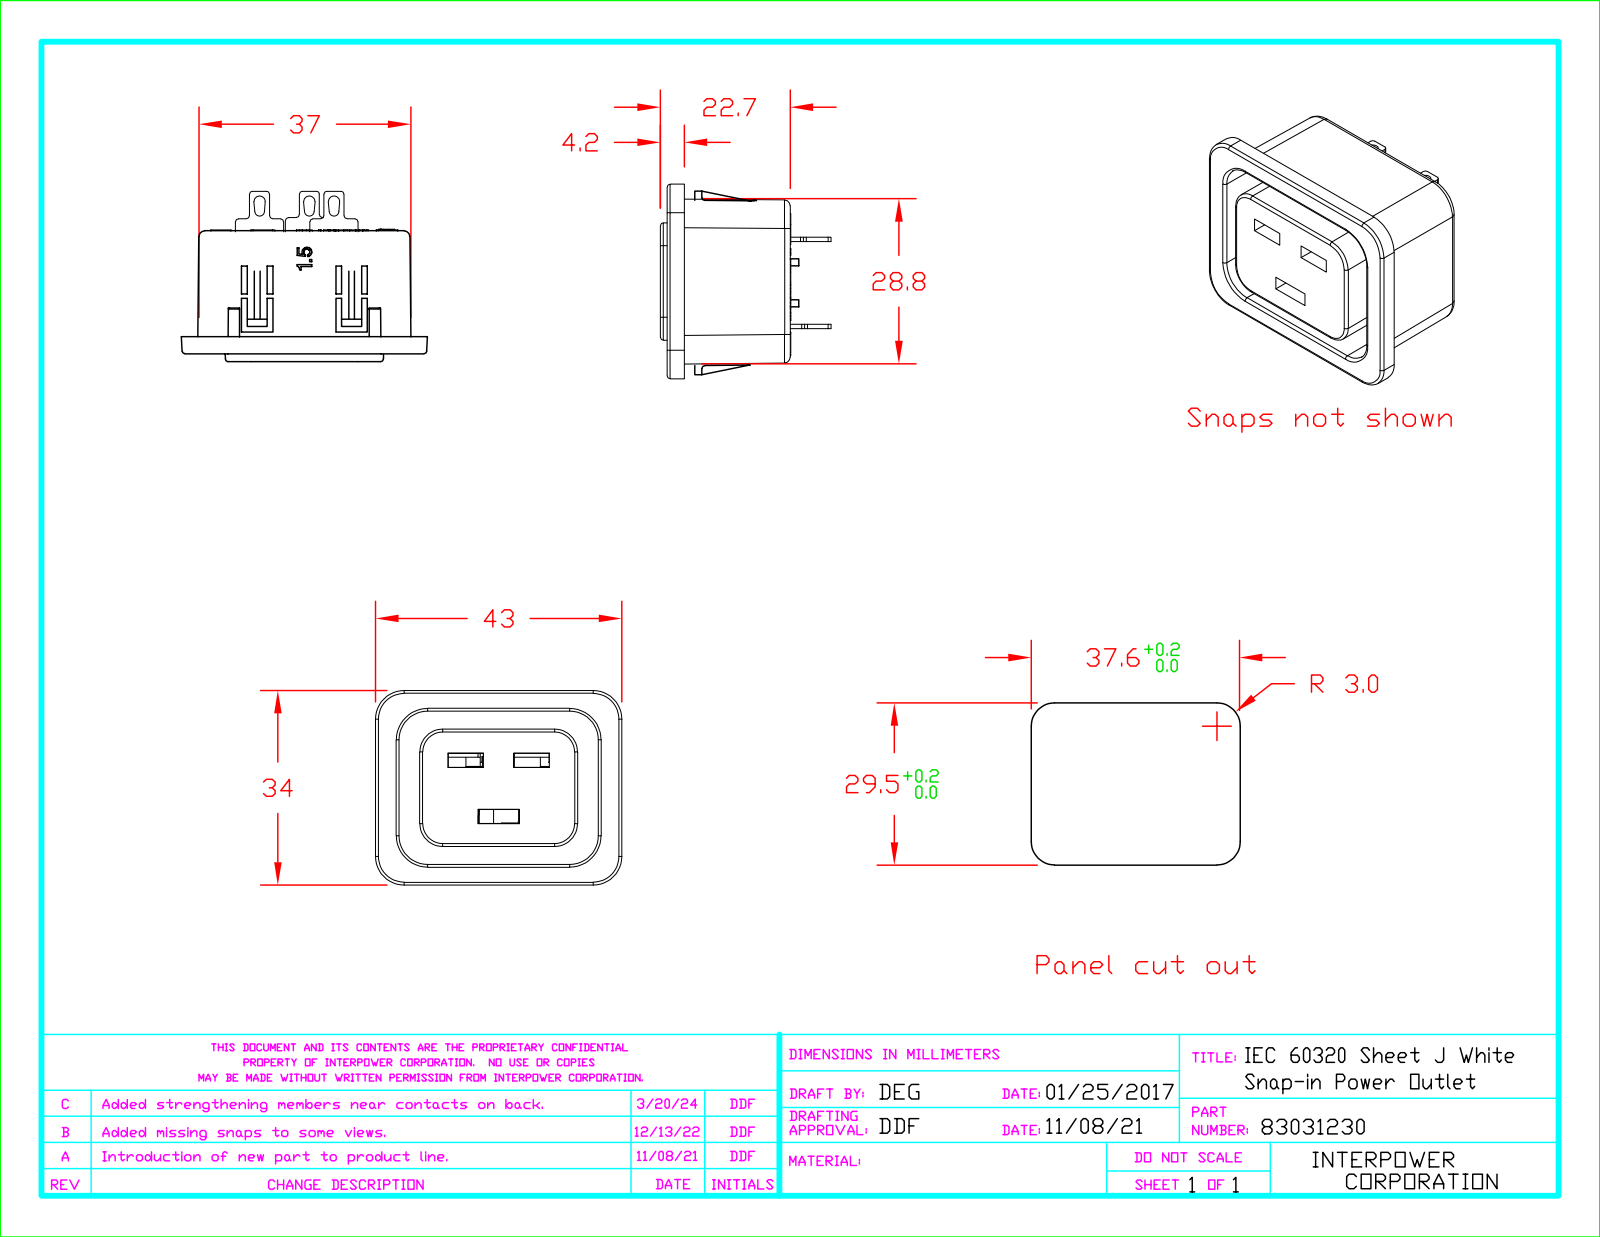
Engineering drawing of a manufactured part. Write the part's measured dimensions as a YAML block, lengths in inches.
part_name: "55020630_R9_Sheet-J_Solder-Tab_2-28-16.2; 55020630_R9_Sheet-J_Solder-Contact_Assy_2-28-16; 68024180_R9_Hsng_Sheet-J_SI-1.5_Solder-Outlet_1-20-17; Part-Number-Insert_83031030 (+1 more)"
step_written_by: "PTC Creo Elements/Direct Modeling 19.0D 23-Nov-2015 (C) Parametric Technology GmbH (AUTOMOTIVE_DESIGN)"
units: inches
bodies: {solids: 5, faces: 1730, planar: 1218, cylindrical: 459, other: 53}
overall_size: [1.693, 1.339, 1.181]
volume: 0.683
surface_area: 24.39
round_holes:
  - {diameter: 0.02, count: 1}
  - {diameter: 0.157, count: 1}
partial_cylinders:
  - {radius: 0.02, count: 55}
  - {radius: 0.016, count: 36}
  - {radius: 0.047, count: 36}
  - {radius: 0.014, count: 14}
  - {radius: 0.009, count: 12}
  - {radius: 0.009, count: 12}
  - {radius: 0.014, count: 12}
  - {radius: 0.029, count: 12}
face_to_face_distances: [0.059, 0.031, 0.787, 0.728, 0.901, 0.931, 0.931, 0.315, 0.172, 0.669]
hole_center_spacings: [0.665]
